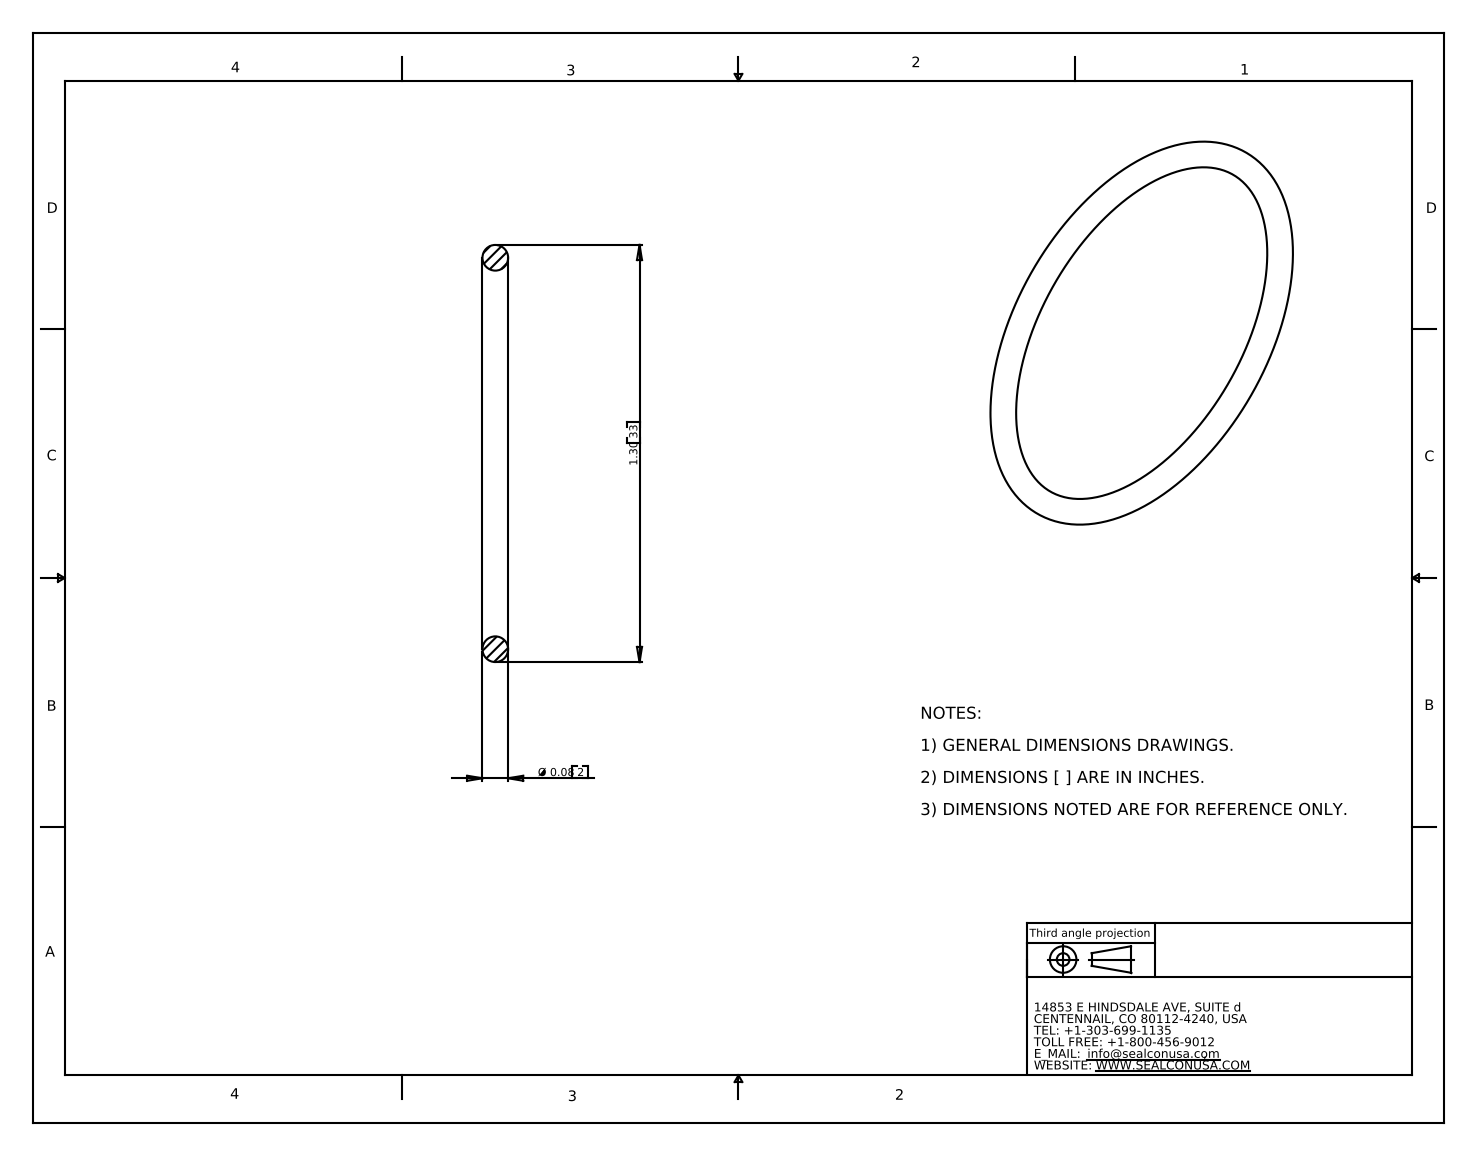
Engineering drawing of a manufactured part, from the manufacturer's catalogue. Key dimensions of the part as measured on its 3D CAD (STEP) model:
Part name (STEP PRODUCT): OR-10-VT
STEP written by: SolidWorks 2007 (CONFIG_CONTROL_DESIGN)
Units: inches
Bodies: 1 solid, 4 faces (0 planar, 0 cylindrical, 4 other)
Overall size (bounding box): 1.3 × 1.3 × 0.08
Volume: 0.019 in³ · Surface area: 0.963 in²
